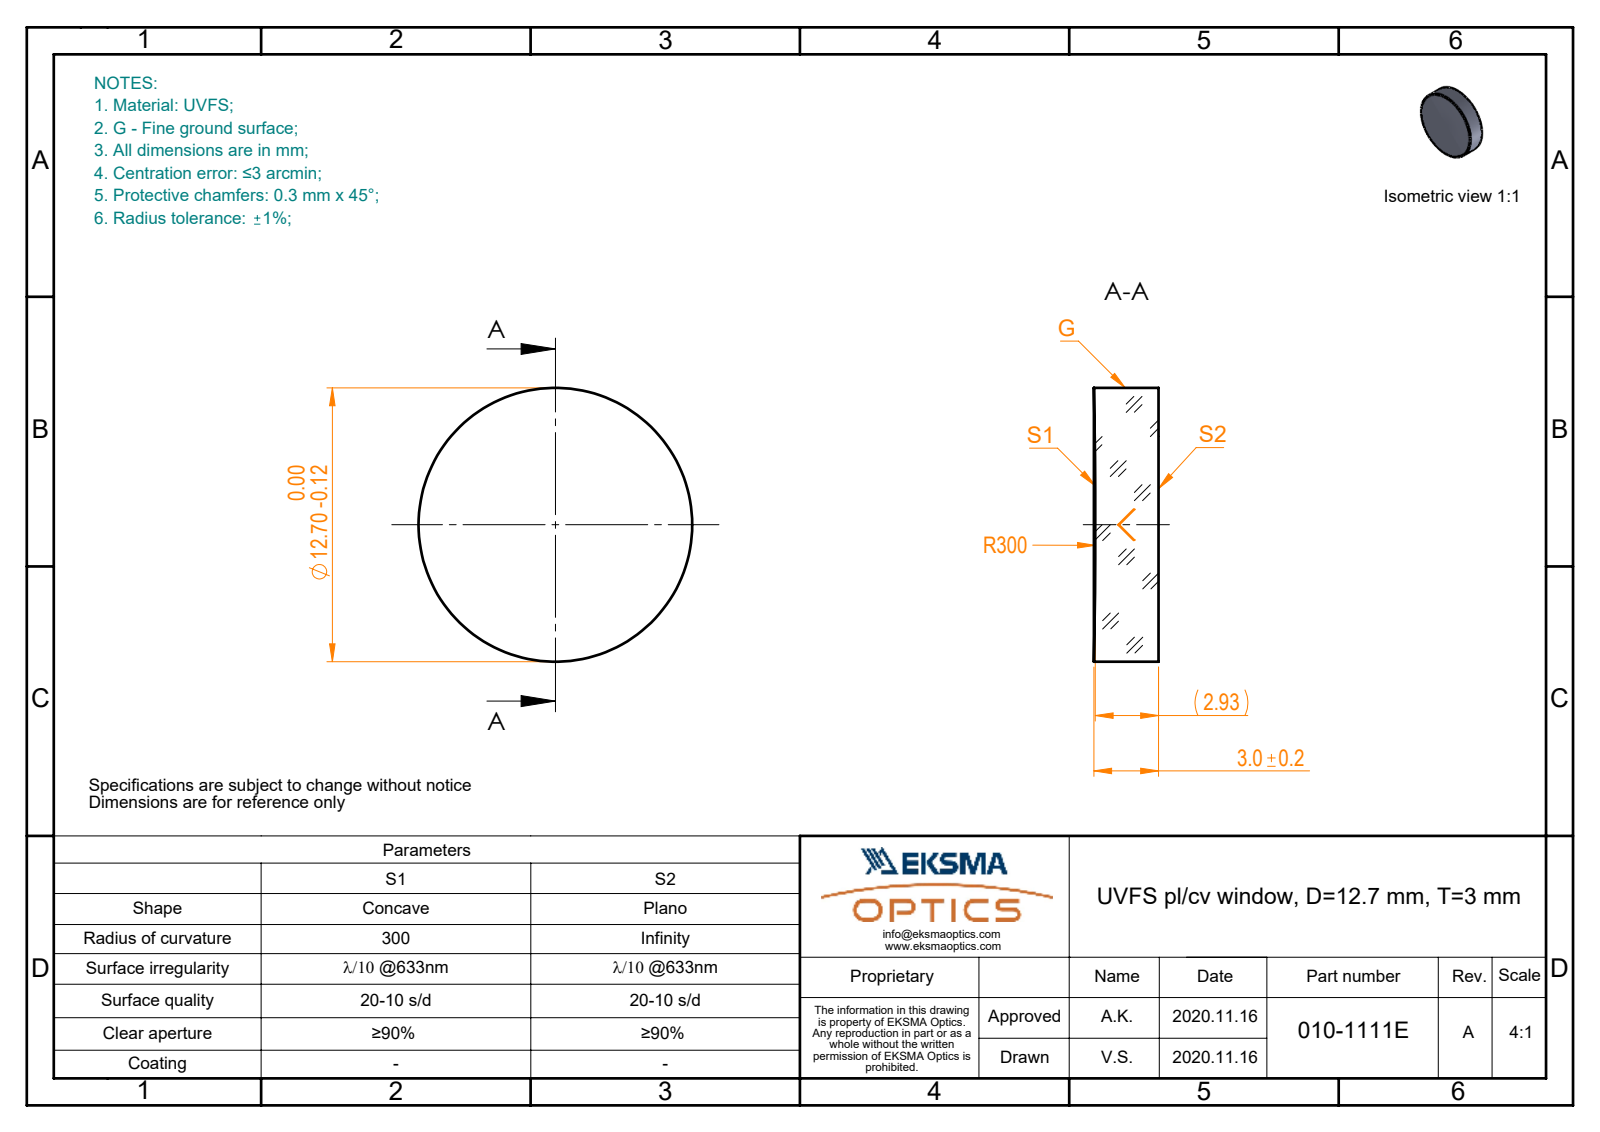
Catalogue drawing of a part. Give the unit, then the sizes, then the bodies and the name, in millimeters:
Units: millimetres
Overall size (bounding box): 12.7 × 12.7 × 3
Round bosses / shafts (diameter × count): ⌀12.7 ×1
Volume: 376 mm³ · Surface area: 373 mm²
Bodies: 1 solid, 5 faces (1 planar, 2 cylindrical, 2 other)
Part name (STEP PRODUCT): 010-1111E_UVFS_PCV_window
STEP written by: SolidWorks 2019 (CONFIG_CONTROL_DESIGN)
